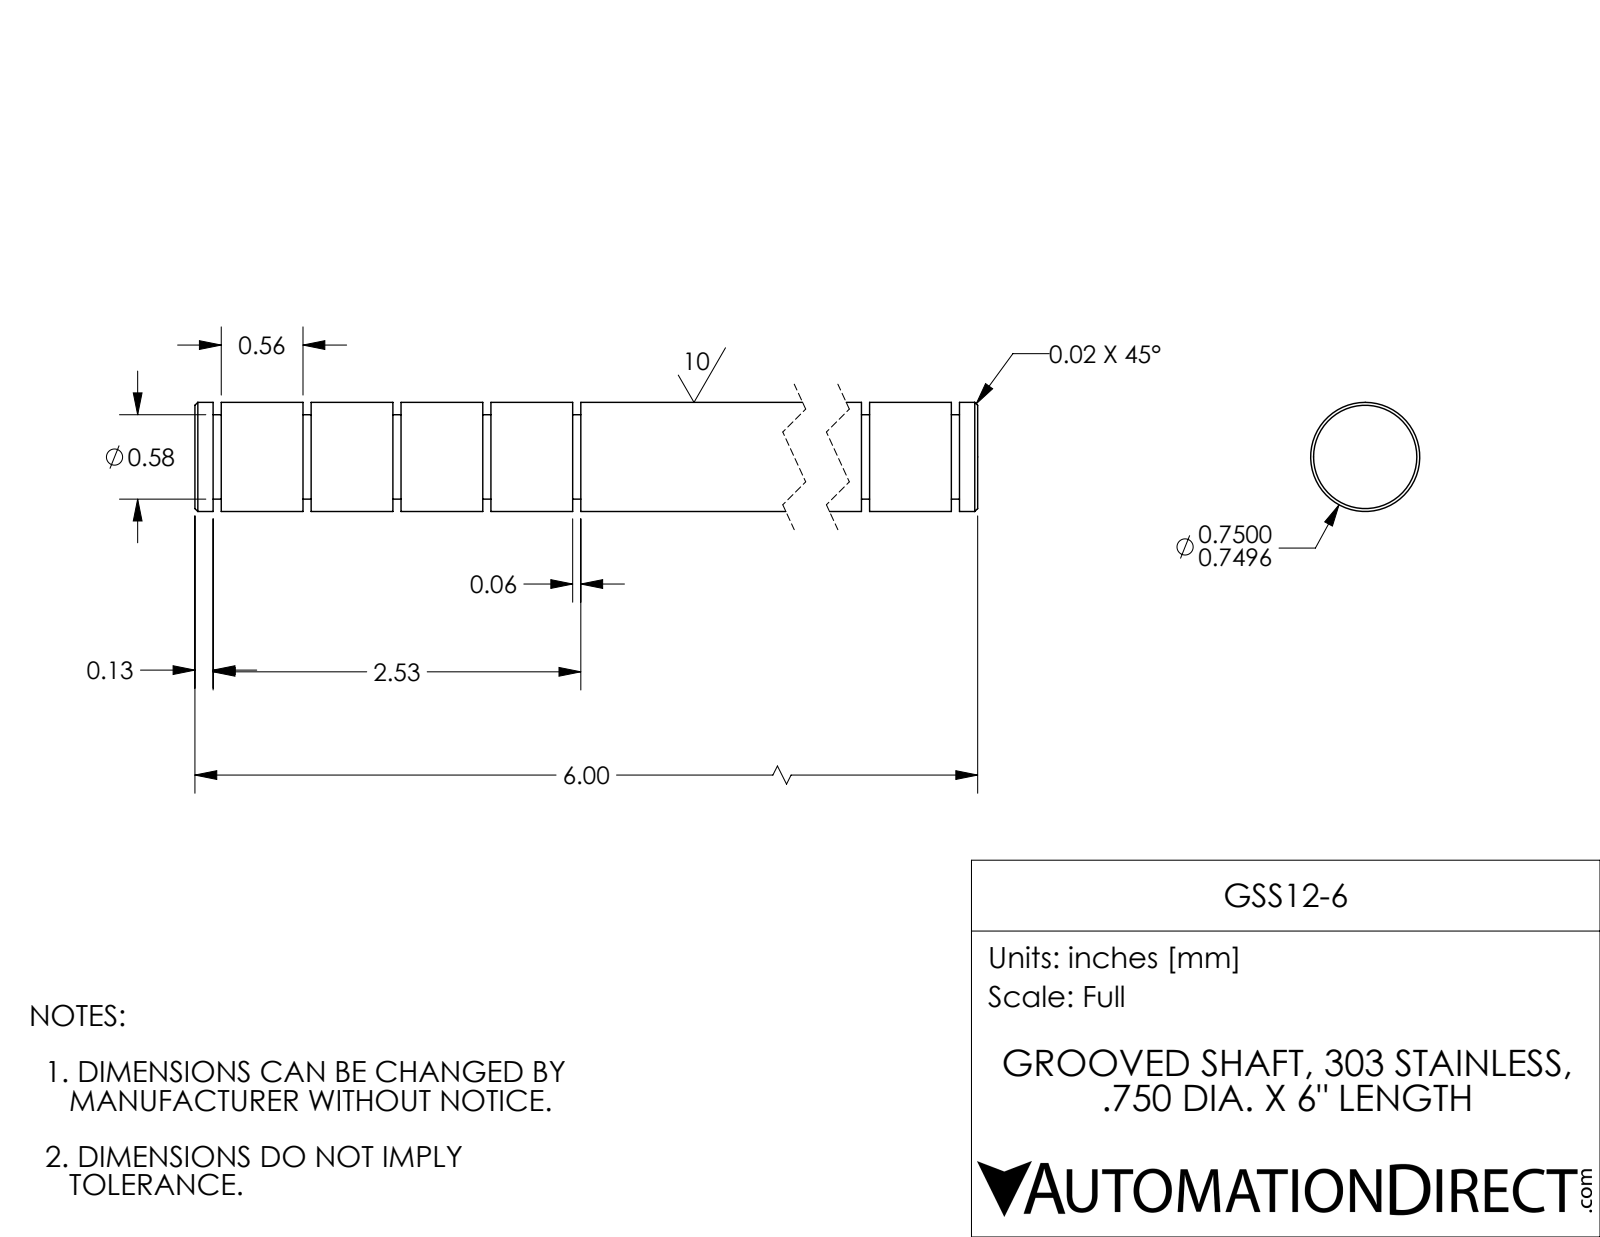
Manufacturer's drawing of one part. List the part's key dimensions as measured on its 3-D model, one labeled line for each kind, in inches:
Part name (STEP PRODUCT): GSS12-6
STEP written by: SolidWorks 2017 (AUTOMOTIVE_DESIGN)
Units: inches
Bodies: 1 solid, 50 faces (16 planar, 30 cylindrical, 4 other)
Overall size (bounding box): 6 × 0.75 × 0.75
Volume: 2.58 in³ · Surface area: 17.24 in²
Round bosses / shafts (diameter × count): ⌀0.75 ×1, ⌀0.58 ×1
Main face-to-face distances: 0.618, 0.056, 0.674, 1.236, 0.618, 1.292, 0.562, 5.076, 3.222, 6
